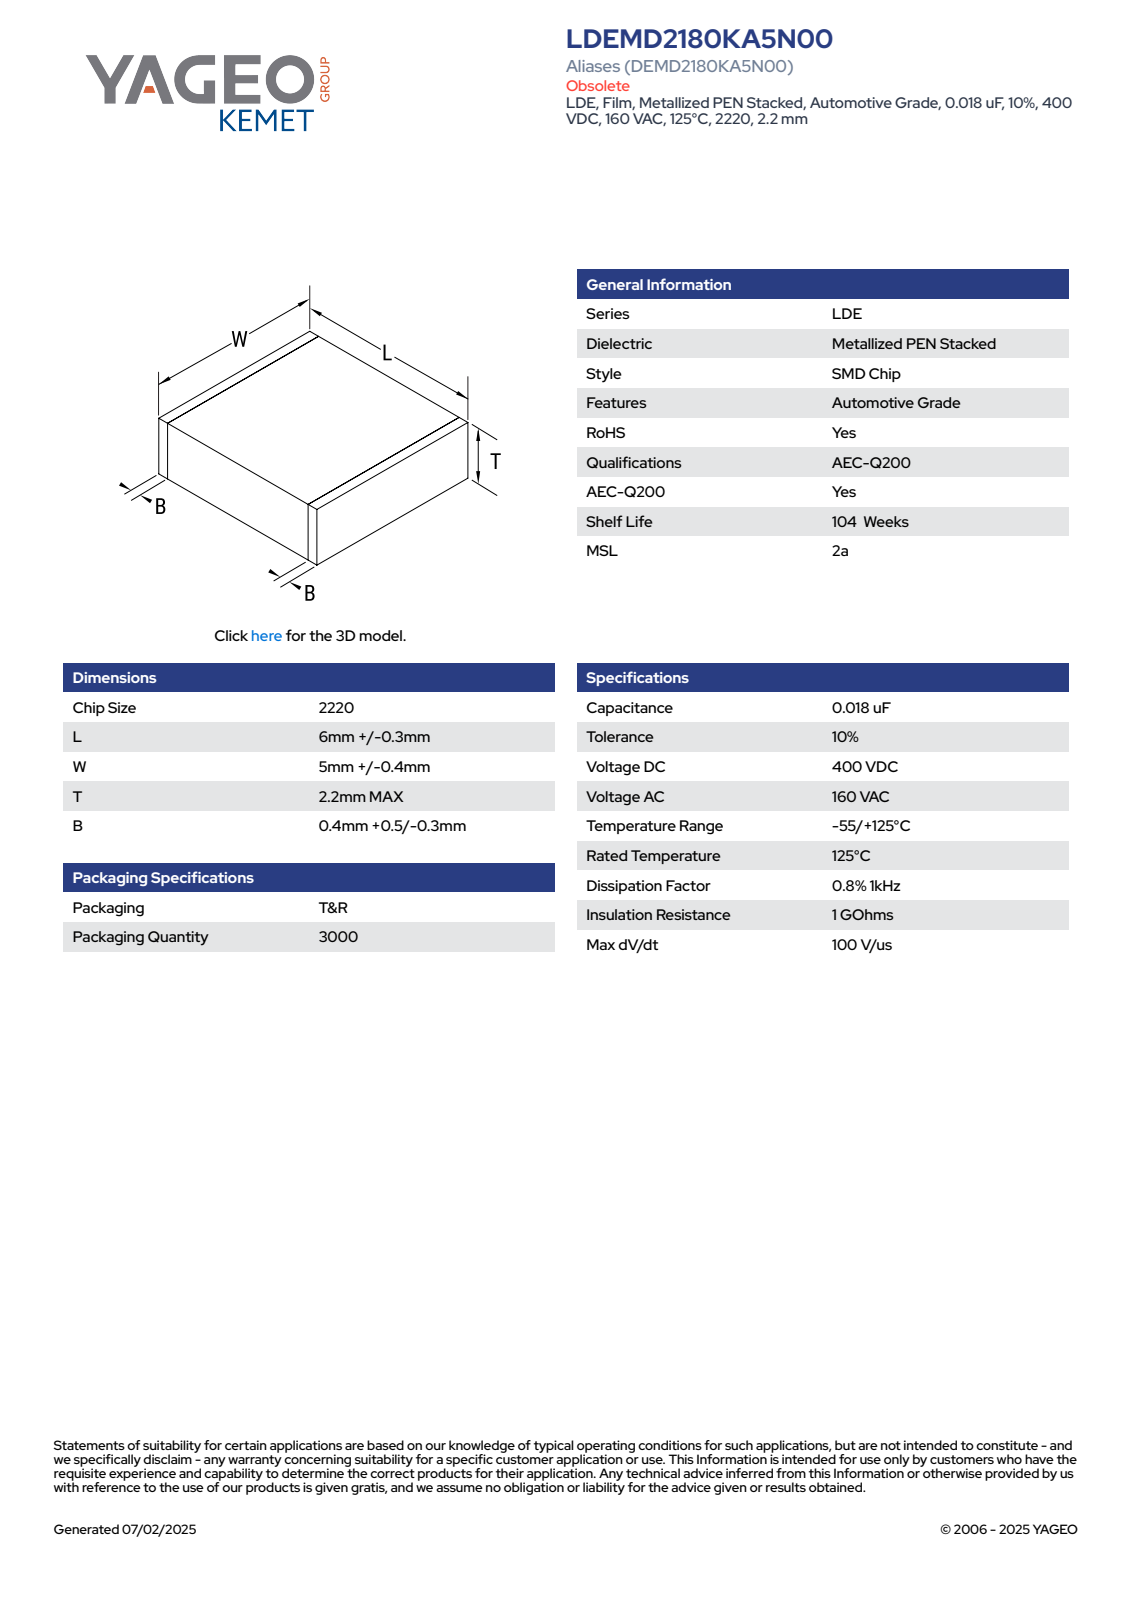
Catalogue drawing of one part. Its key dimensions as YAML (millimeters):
part_name: "CFS_LDELDB_2220_L6.3W5.4T2.2B0.9"
step_written_by: "SolidWorks 2020 (AUTOMOTIVE_DESIGN)"
units: millimeters
bodies: {solids: 4, faces: 73, planar: 73, cylindrical: 0, other: 0}
overall_size: [6.3, 5.4, 2.2]
volume: 74
surface_area: 121
face_to_face_distances: [2.18, 6.3, 5.38, 2.19, 2.2, 5.39, 5.4, 0.5, 5.8, 5.3]
